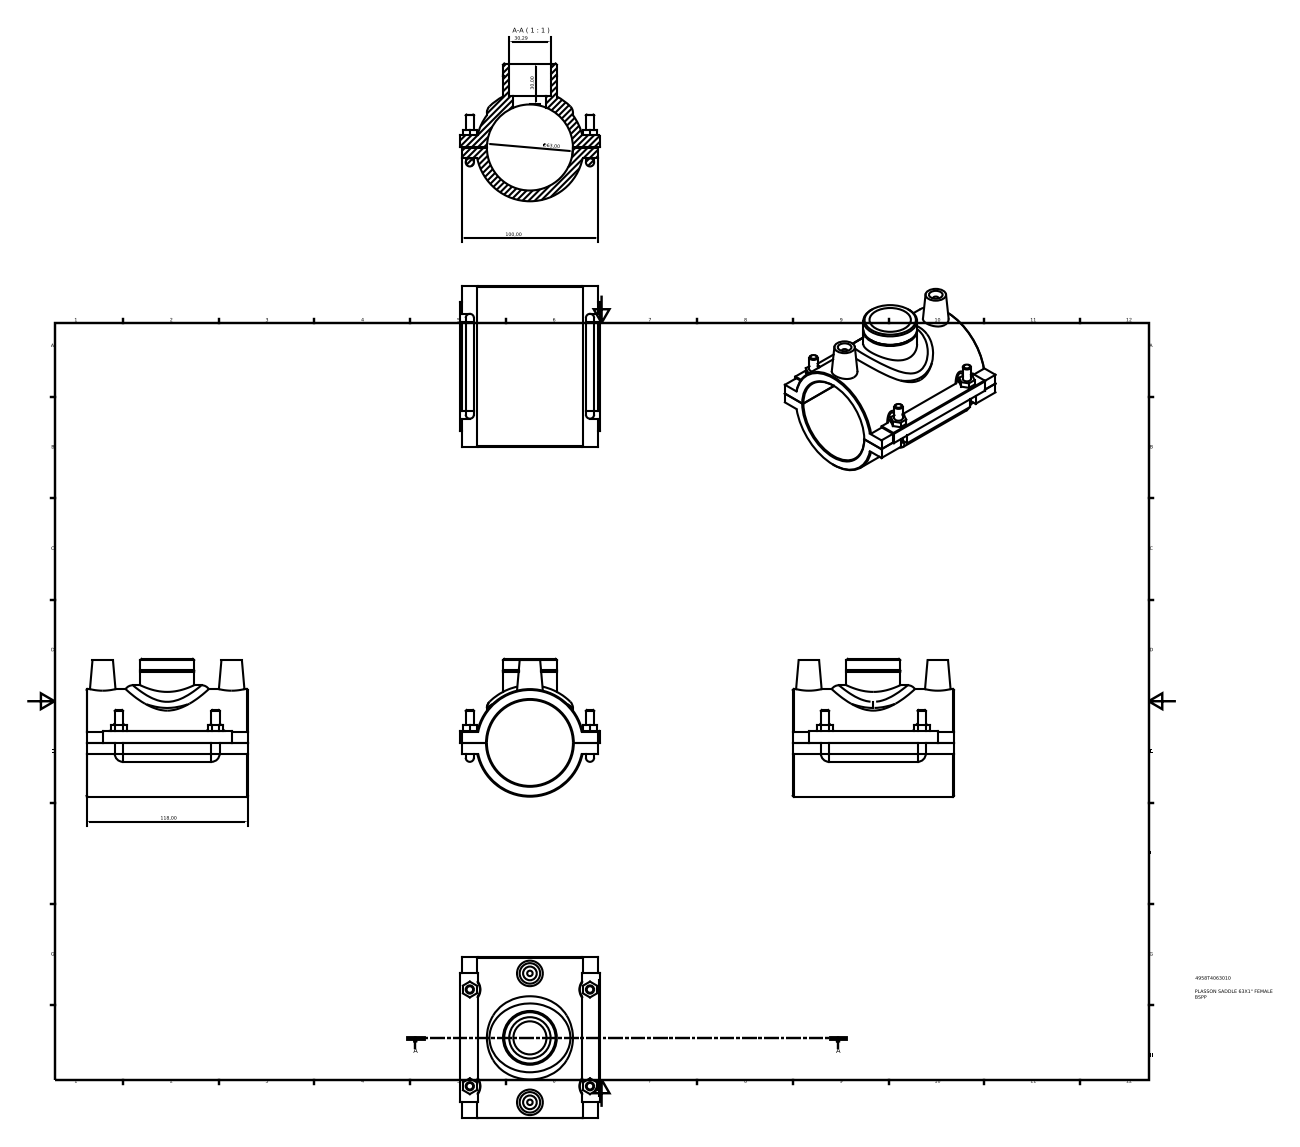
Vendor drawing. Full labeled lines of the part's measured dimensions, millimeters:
Part name (STEP PRODUCT): 4958T4063010
STEP written by: Autodesk Inventor 2015 (AUTOMOTIVE_DESIGN)
Units: millimetres
Bodies: 1 solid, 139 faces (82 planar, 31 cylindrical, 26 other)
Overall size (bounding box): 118 × 102 × 100.88
Volume: 277 946 mm³ · Surface area: 83 347 mm²
Round holes (diameter × count): ⌀10 ×2, ⌀24.23 ×1, ⌀30.29 ×1, ⌀63 ×1
Round bosses / shafts (diameter × count): ⌀6 ×6, ⌀4 ×2, ⌀78.75 ×1, ⌀39.38 ×1, ⌀38.38 ×1
Partial cylindrical surfaces — rounded edges, fillets, slot ends (radius × count): R7.5 ×4, R0.5 ×1, R31.5 ×1, R42.21 ×1
Main face-to-face distances: 7.83, 7.93, 1, 16.75, 8.92, 8.82, 118, 101, 100, 102
Hole centre spacings: 47.2, 94.4
